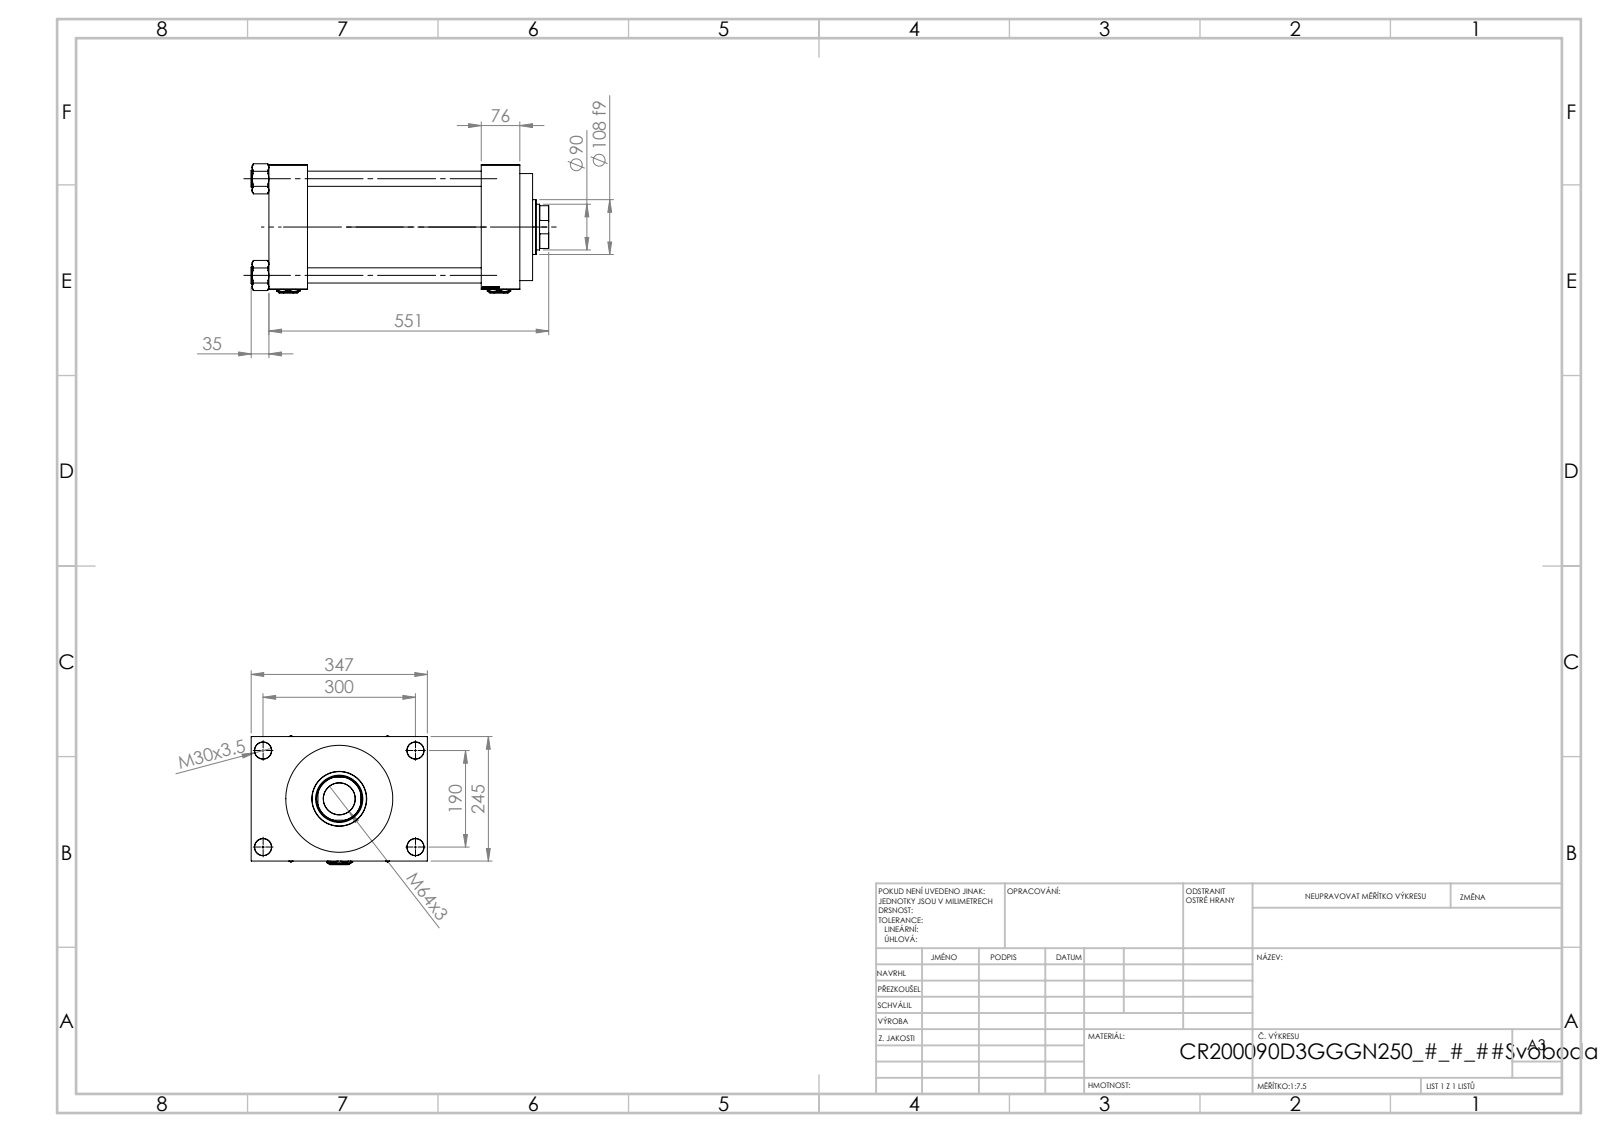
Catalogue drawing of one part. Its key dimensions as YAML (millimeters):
part_name: "V215_VC_A; Zatka_pro_OIL_PORT; V215CR_VCP_D; V215CR_D_TYCINKA (+2 more)"
step_written_by: "SolidWorks 2019 (CONFIG_CONTROL_DESIGN)"
units: millimeters
bodies: {solids: 13, faces: 1249, planar: 591, cylindrical: 98, other: 560}
overall_size: [586, 347, 254.22]
volume: 17200000
surface_area: 1552000
round_holes:
  - {diameter: 30, count: 4}
  - {diameter: 33, count: 4}
  - {diameter: 7, count: 2}
  - {diameter: 41.92, count: 2}
  - {diameter: 52, count: 2}
  - {diameter: 62.5, count: 1}
  - {diameter: 90, count: 1}
  - {diameter: 93, count: 1}
  - {diameter: 146, count: 1}
  - {diameter: 200, count: 1}
  - {diameter: 210.5, count: 1}
round_bosses_or_shafts:
  - {diameter: 33, count: 4}
  - {diameter: 206, count: 1}
  - {diameter: 108, count: 1}
partial_cylinders:
  - {radius: 44, count: 1}
face_to_face_distances: [76, 418, 342, 245, 494, 475.74, 399.74, 57.74, 18.26, 51]
hole_center_spacings: [54.9, 134.49, 177.55, 190.2, 197.87, 245.1, 310.18, 190]
